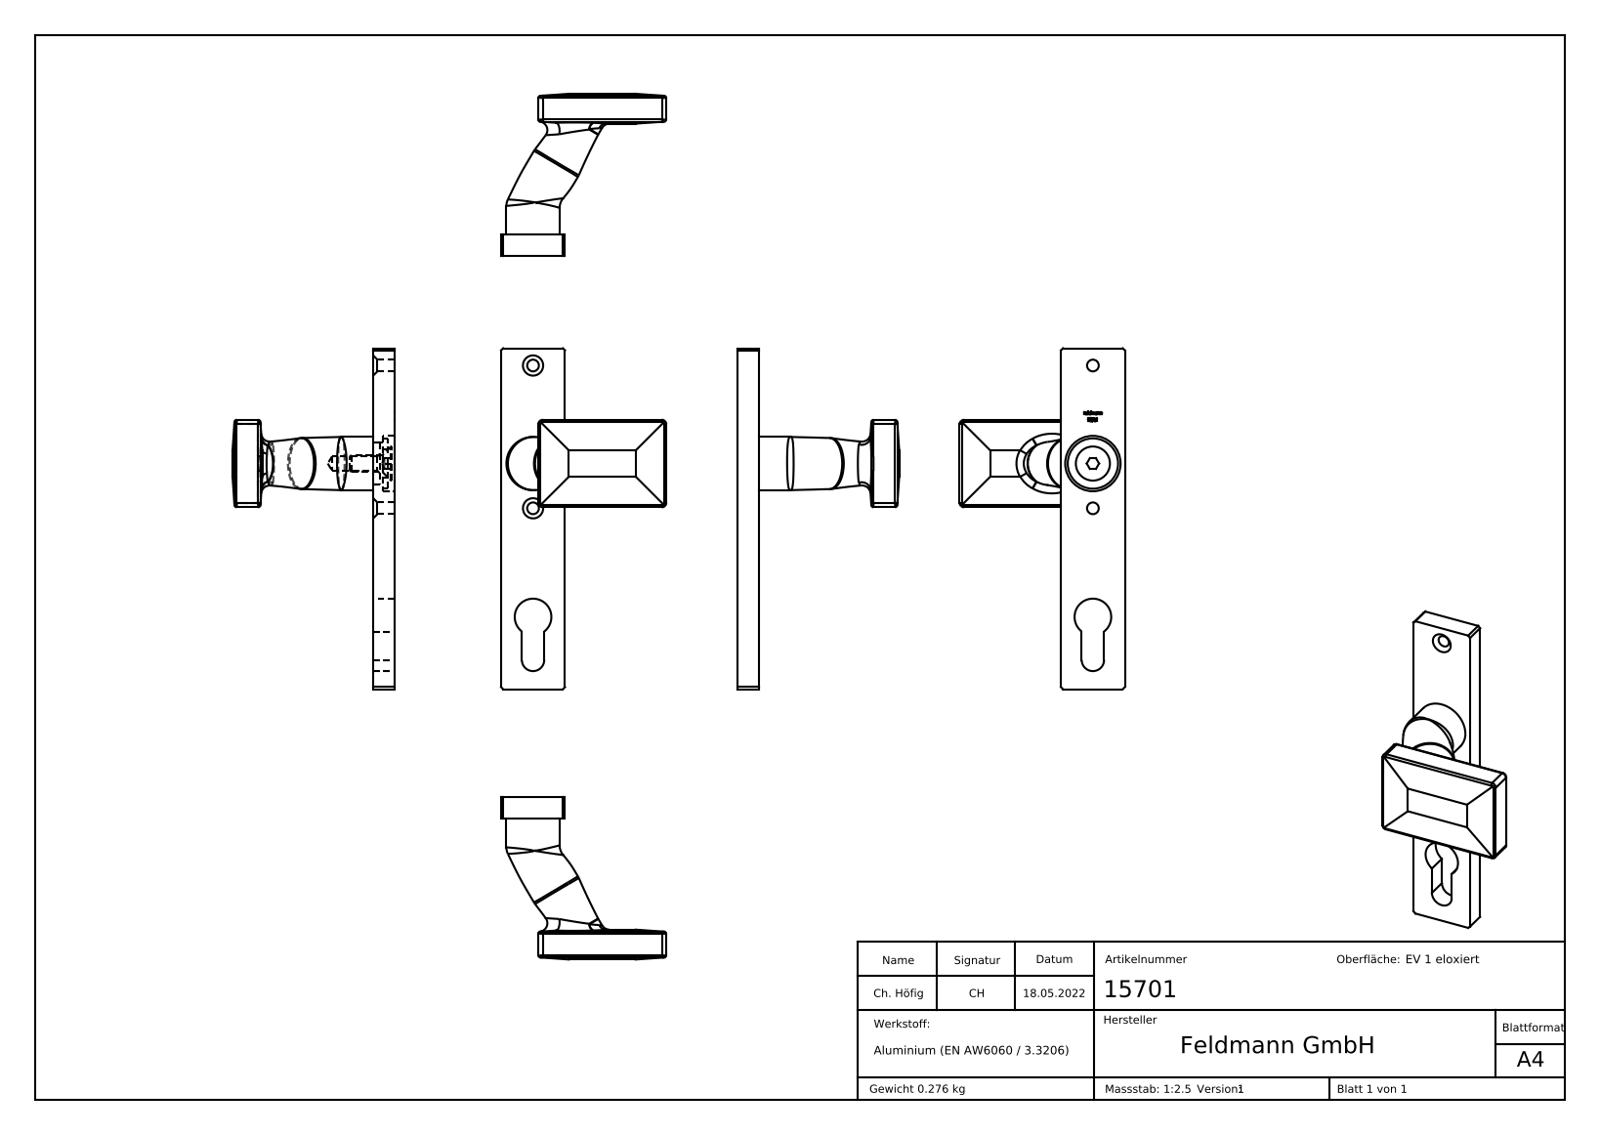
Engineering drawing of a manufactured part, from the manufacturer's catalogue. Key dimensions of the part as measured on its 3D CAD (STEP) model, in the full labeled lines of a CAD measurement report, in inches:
Part name (STEP PRODUCT): DIN 7991 Konfig_M8x20; 15701 Teil3_15701 Teil3; 15701; 15701 Teil2_15701 Teil2 (+1 more)
STEP written by: SolidWorks 2018 (CONFIG_CONTROL_DESIGN)
Units: inches
Bodies: 4 solids, 266 faces (135 planar, 27 cylindrical, 104 other)
Overall size (bounding box): 6.299 × 3.051 × 2.992
Volume: 6.009 in³ · Surface area: 42.83 in²
Round holes (diameter × count): ⌀0.217 ×2, ⌀0.268 ×1, ⌀0.512 ×1, ⌀0.787 ×1, ⌀1.024 ×1
Round bosses / shafts (diameter × count): ⌀0.984 ×1, ⌀0.929 ×1, ⌀0.768 ×1, ⌀0.63 ×1, ⌀0.315 ×1
Partial cylindrical surfaces — rounded edges, fillets, slot ends (radius × count): R0.039 ×8, R0.079 ×4, R0.207 ×1, R0.339 ×1, R0.394 ×1
Main face-to-face distances: 0.394, 1.181, 1.614, 0.177, 0.217, 0.585, 0.584, 2.992, 2.776, 2.598
Hole centre spacings: 0.827, 1.811, 2.638
